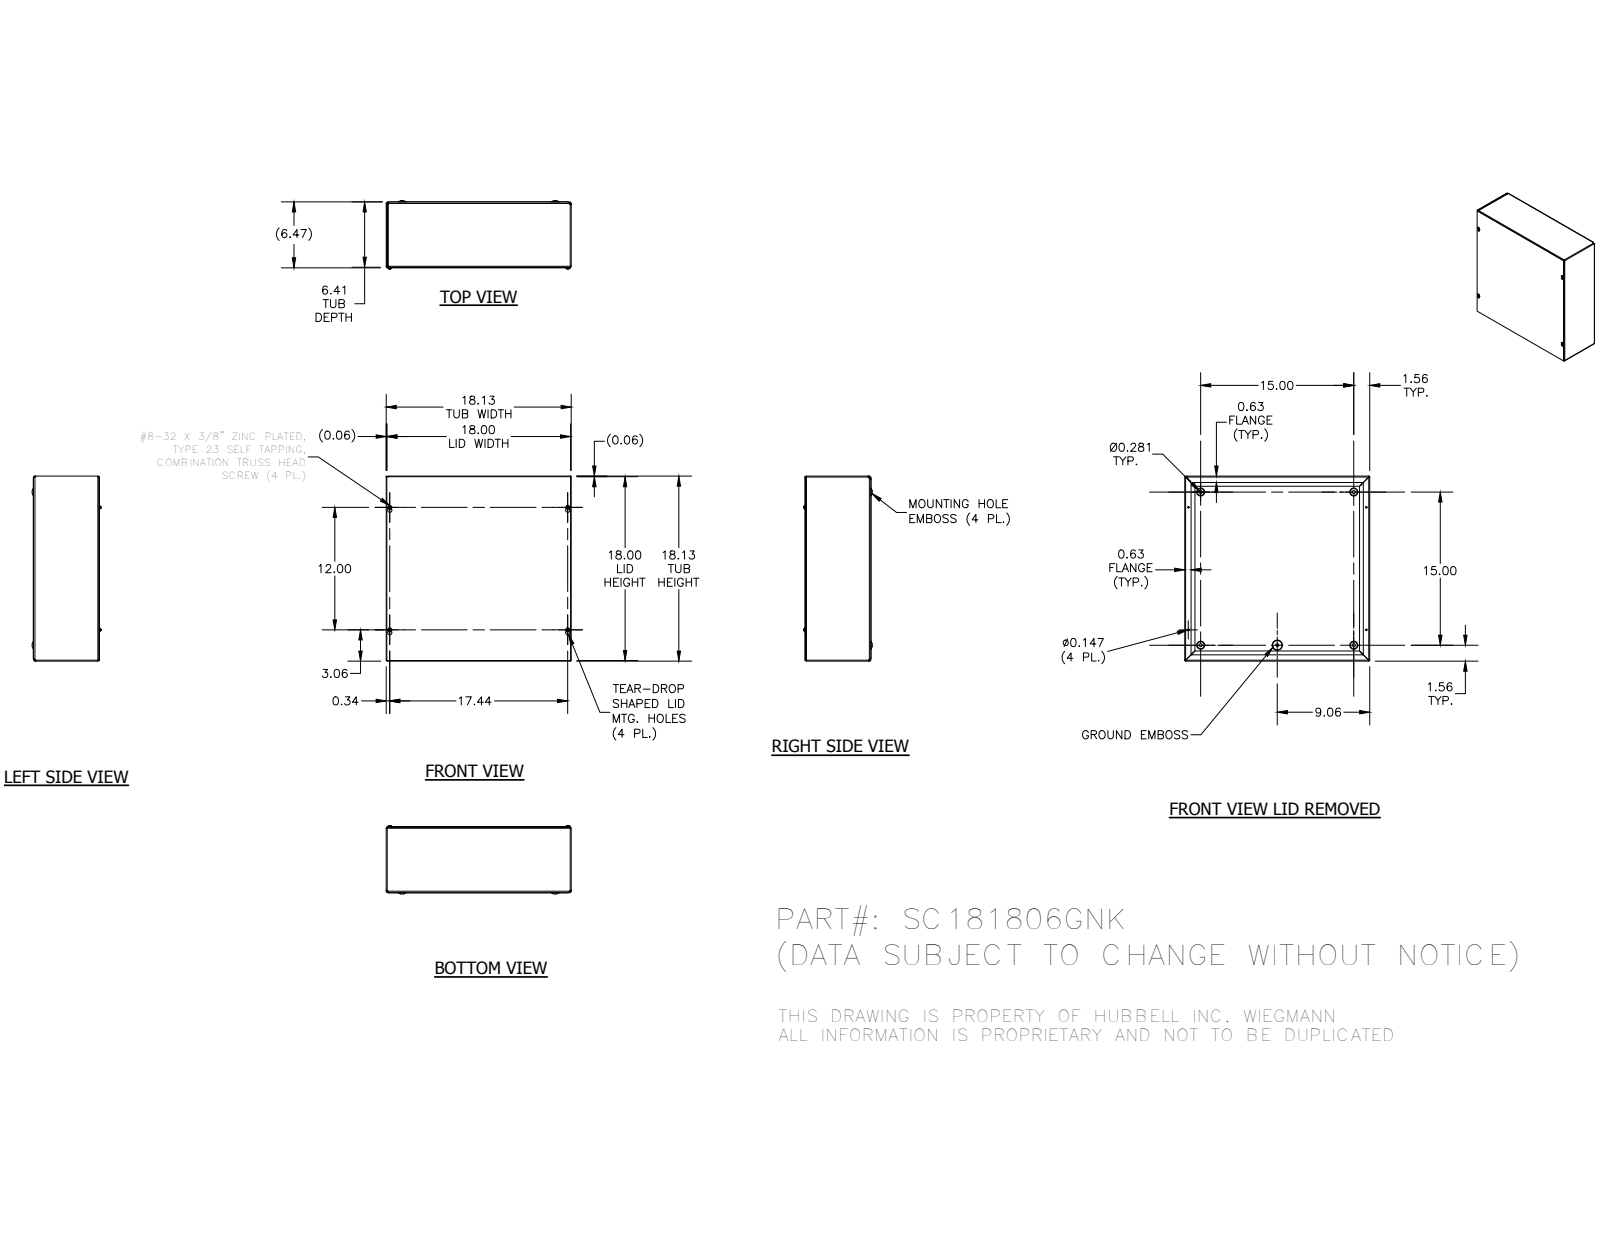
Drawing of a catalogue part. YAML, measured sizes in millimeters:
part_name: "SC1818GNKBKP; SC181806GNKWRA; SC1818GNKLID; 34056 (+1 more)"
step_written_by: "Autodesk Inventor 2014 (AUTOMOTIVE_DESIGN)"
units: millimeters
bodies: {solids: 7, faces: 358, planar: 133, cylindrical: 73, other: 152}
overall_size: [460.38, 460.38, 170]
volume: 1221000
surface_area: 1560000
round_holes:
  - {diameter: 3.73, count: 4}
  - {diameter: 7.62, count: 4}
  - {diameter: 4.19, count: 1}
round_bosses_or_shafts:
  - {diameter: 9.75, count: 4}
  - {diameter: 4.17, count: 4}
  - {diameter: 5.8, count: 1}
partial_cylinders:
  - {radius: 0.79, count: 8}
  - {radius: 2.37, count: 8}
  - {radius: 1.4, count: 4}
  - {radius: 1.57, count: 4}
  - {radius: 2.38, count: 4}
  - {radius: 2.97, count: 4}
  - {radius: 3.15, count: 4}
  - {radius: 3.17, count: 4}
face_to_face_distances: [1.57, 161.12, 458.8, 162.69, 1.59, 162.71, 164.28, 457.23, 1.58, 460.38]
hole_center_spacings: [381, 190.5, 304.8, 344.27, 344.31, 413.71, 413.72, 425.97]
